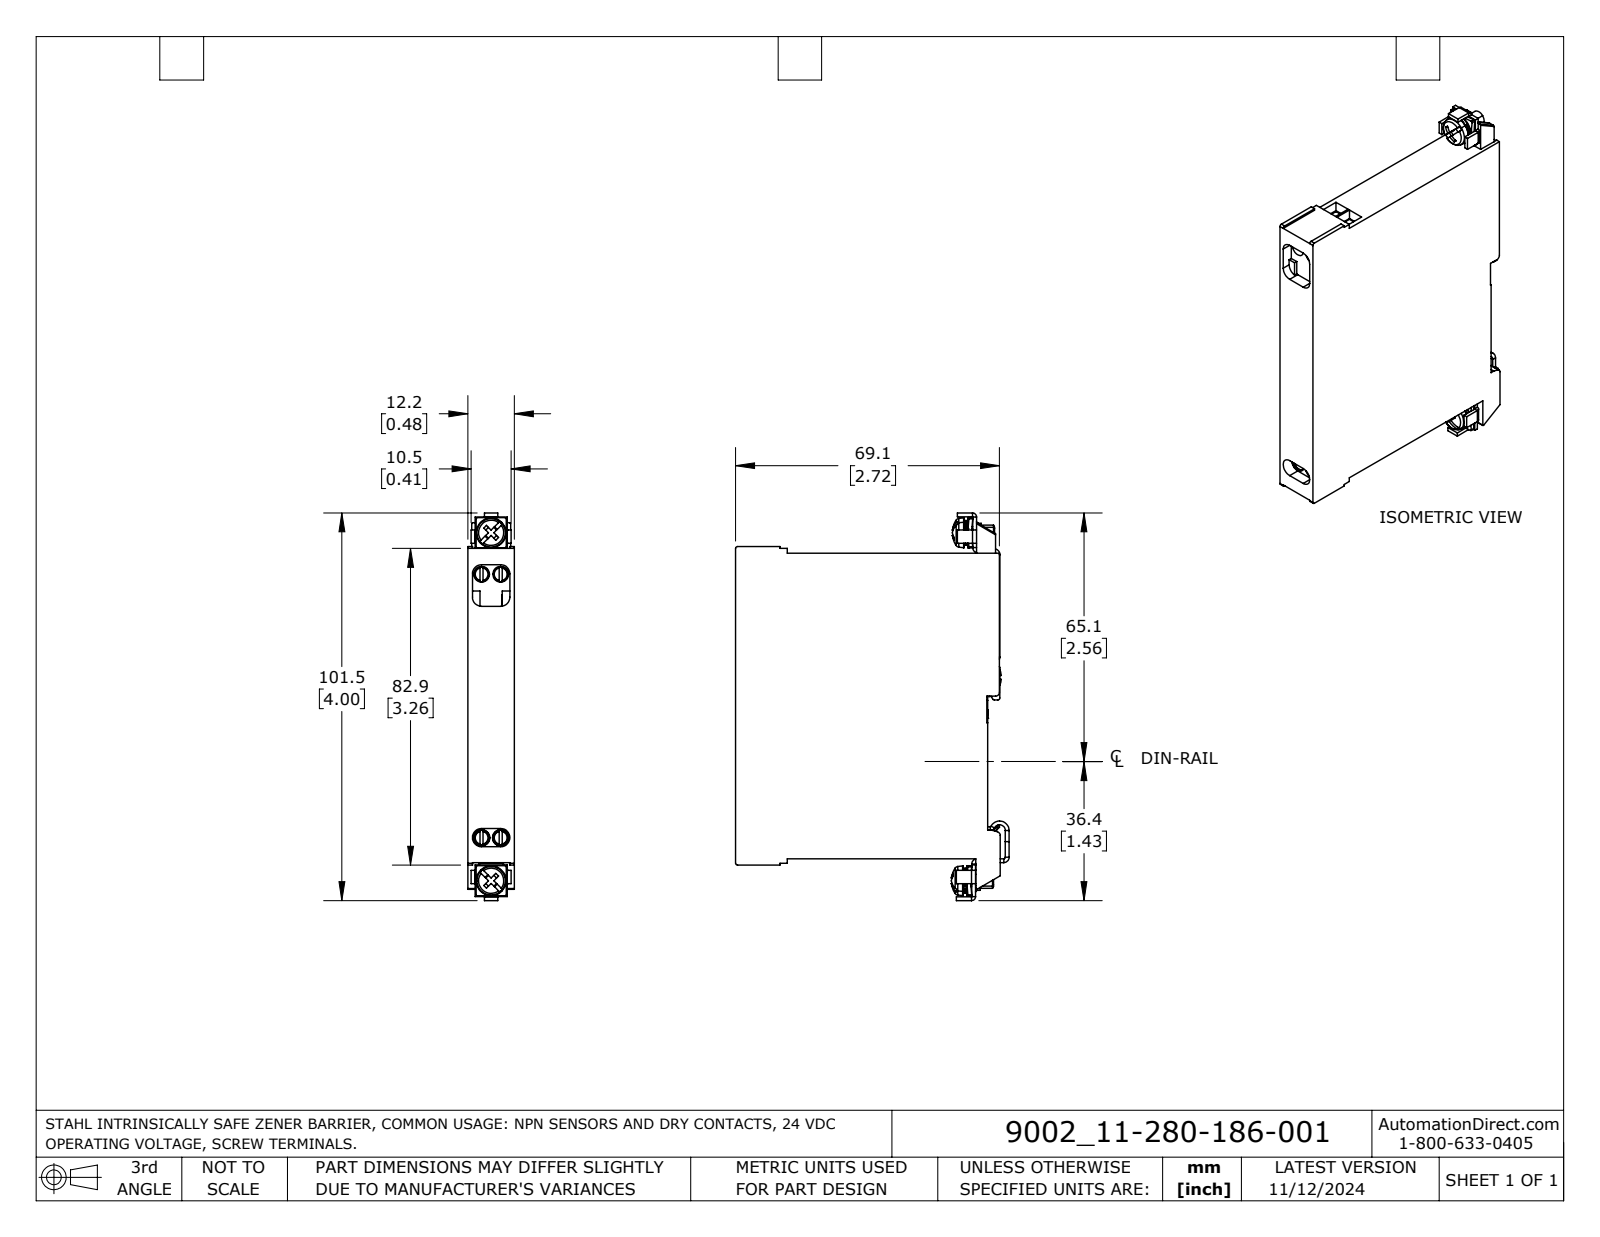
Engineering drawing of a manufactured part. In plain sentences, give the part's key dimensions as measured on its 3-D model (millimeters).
The part is named "900211-280-186-001". Its 3-D file was written by "SolidWorks 2023 (AUTOMOTIVE_DESIGN)". It is 4 solids with 762 faces: 528 planar, 146 cylindrical and 88 other. Overall it measures 101.5 by 71.6 by 12.2 millimeters. Its volume is 65 250 cubic millimeters and its surface area 21 750 square millimeters. Round holes: 4 of diameter 4.1, 3 of diameter 4.3, 2 of diameter 3.3, 2 of diameter 4.2, 1 of diameter 3. Round bosses or shafts: 3 of diameter 7.8, 3 of diameter 4, 2 of diameter 5, 2 of diameter 3.1, 1 of diameter 6.5. Partial cylindrical surfaces (rounded edges, fillets, slot ends): 16 of radius 0.5, 8 of radius 0.3, 6 of radius 0.4, 6 of radius 1, 6 of radius 1, 6 of radius 1.4, 6 of radius 2.4, 4 of radius 0.3. The main face-to-face distances are 12.2, 1, 79, 1.1, 2, 78, 2.2, 80, 2.1, 1.2. The hole center spacings are 5, 11.1, 11.5, 27.1, 28.2, 41, 42.1, 69.
